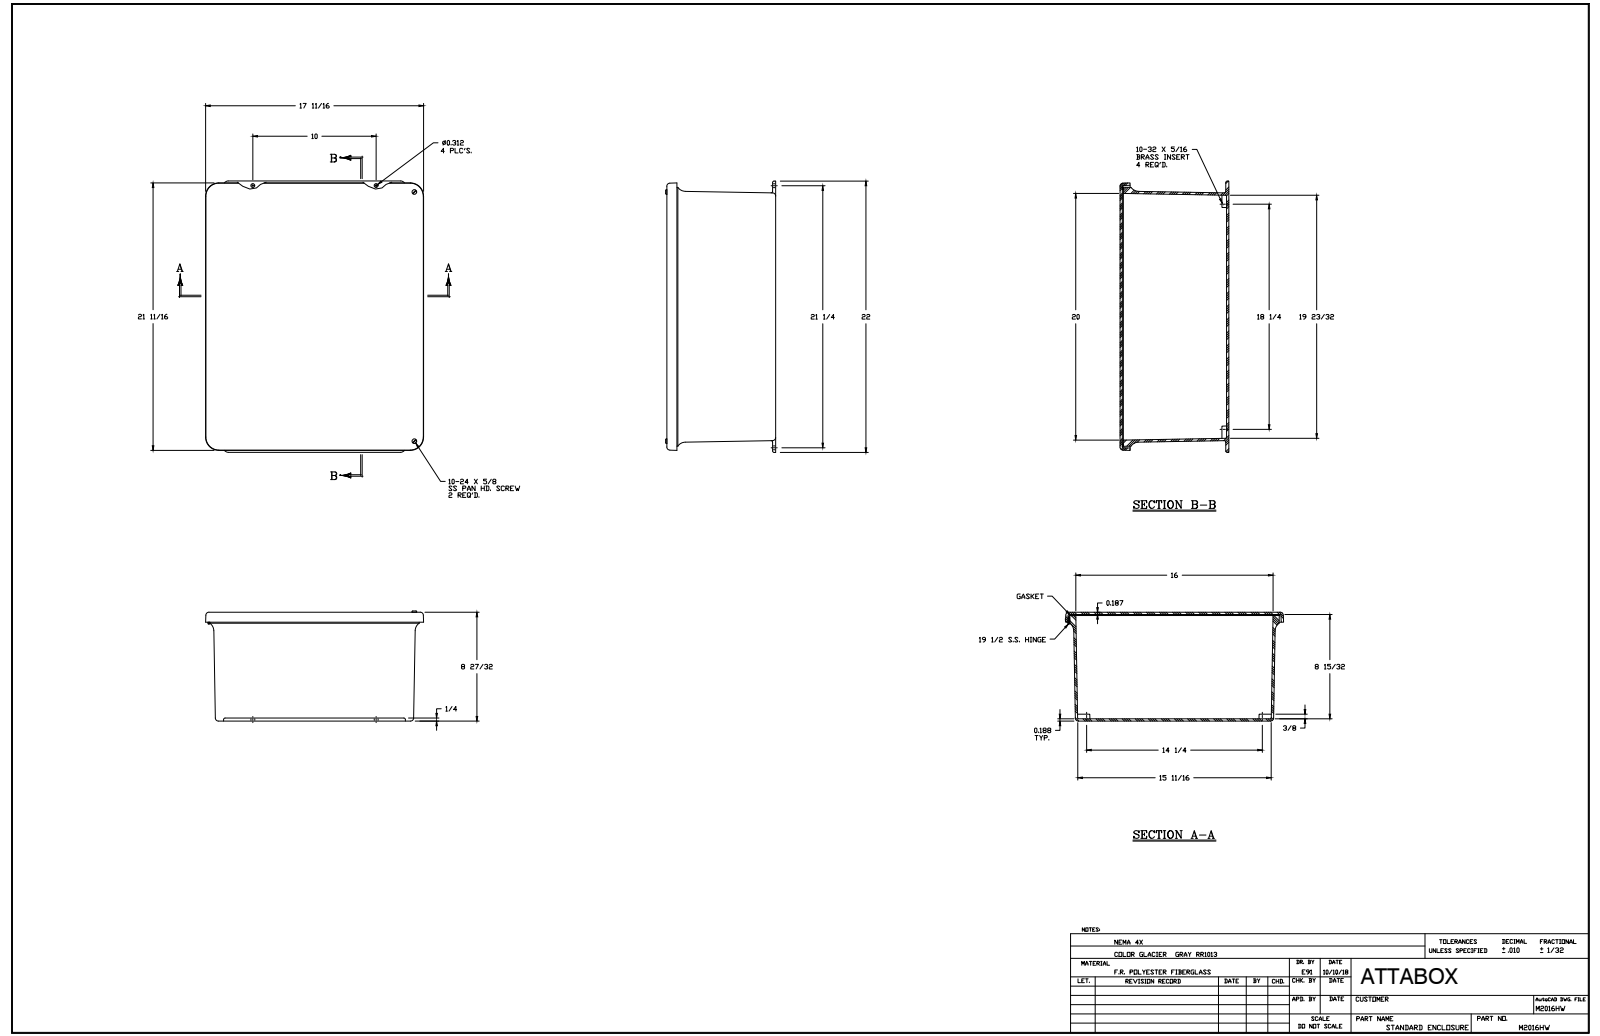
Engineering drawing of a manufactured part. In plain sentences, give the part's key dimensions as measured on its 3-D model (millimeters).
The part is named "M2016HW". Its 3-D file was written by "SolidWorks 2018 (AUTOMOTIVE_DESIGN)". It is 26 solids with 985 faces: 393 planar, 387 cylindrical and 205 other. Overall it measures 558.8 by 449.9 by 227.6 millimeters. Its volume is 4 636 000 cubic millimeters and its surface area 1 896 000 square millimeters. Round holes: 12 of diameter 3.3, 12 of diameter 3.6, 5 of diameter 3.9, 4 of diameter 4, 4 of diameter 5.5, 2 of diameter 3.7, 1 of diameter 2.2. Round bosses or shafts: 12 of diameter 6.4, 7 of diameter 3.2, 6 of diameter 6.9, 5 of diameter 3.2, 2 of diameter 4.8, 2 of diameter 4, 1 of diameter 3.9, 1 of diameter 3.9. Partial cylindrical surfaces (rounded edges, fillets, slot ends): 20 of radius 0.8, 10 of radius 3.2, 8 of radius 6.4, 7 of radius 5.1, 4 of radius 1.6, 4 of radius 9.5, 4 of radius 19.1. The main face-to-face distances are 4.7, 219.5, 224.3, 4.8, 214.7, 219.5, 8, 12.7, 217.5, 212.7. The hole center spacings are 95.3, 190.5, 6.4, 88.9, 101.6, 184.2, 196.9, 279.4.
